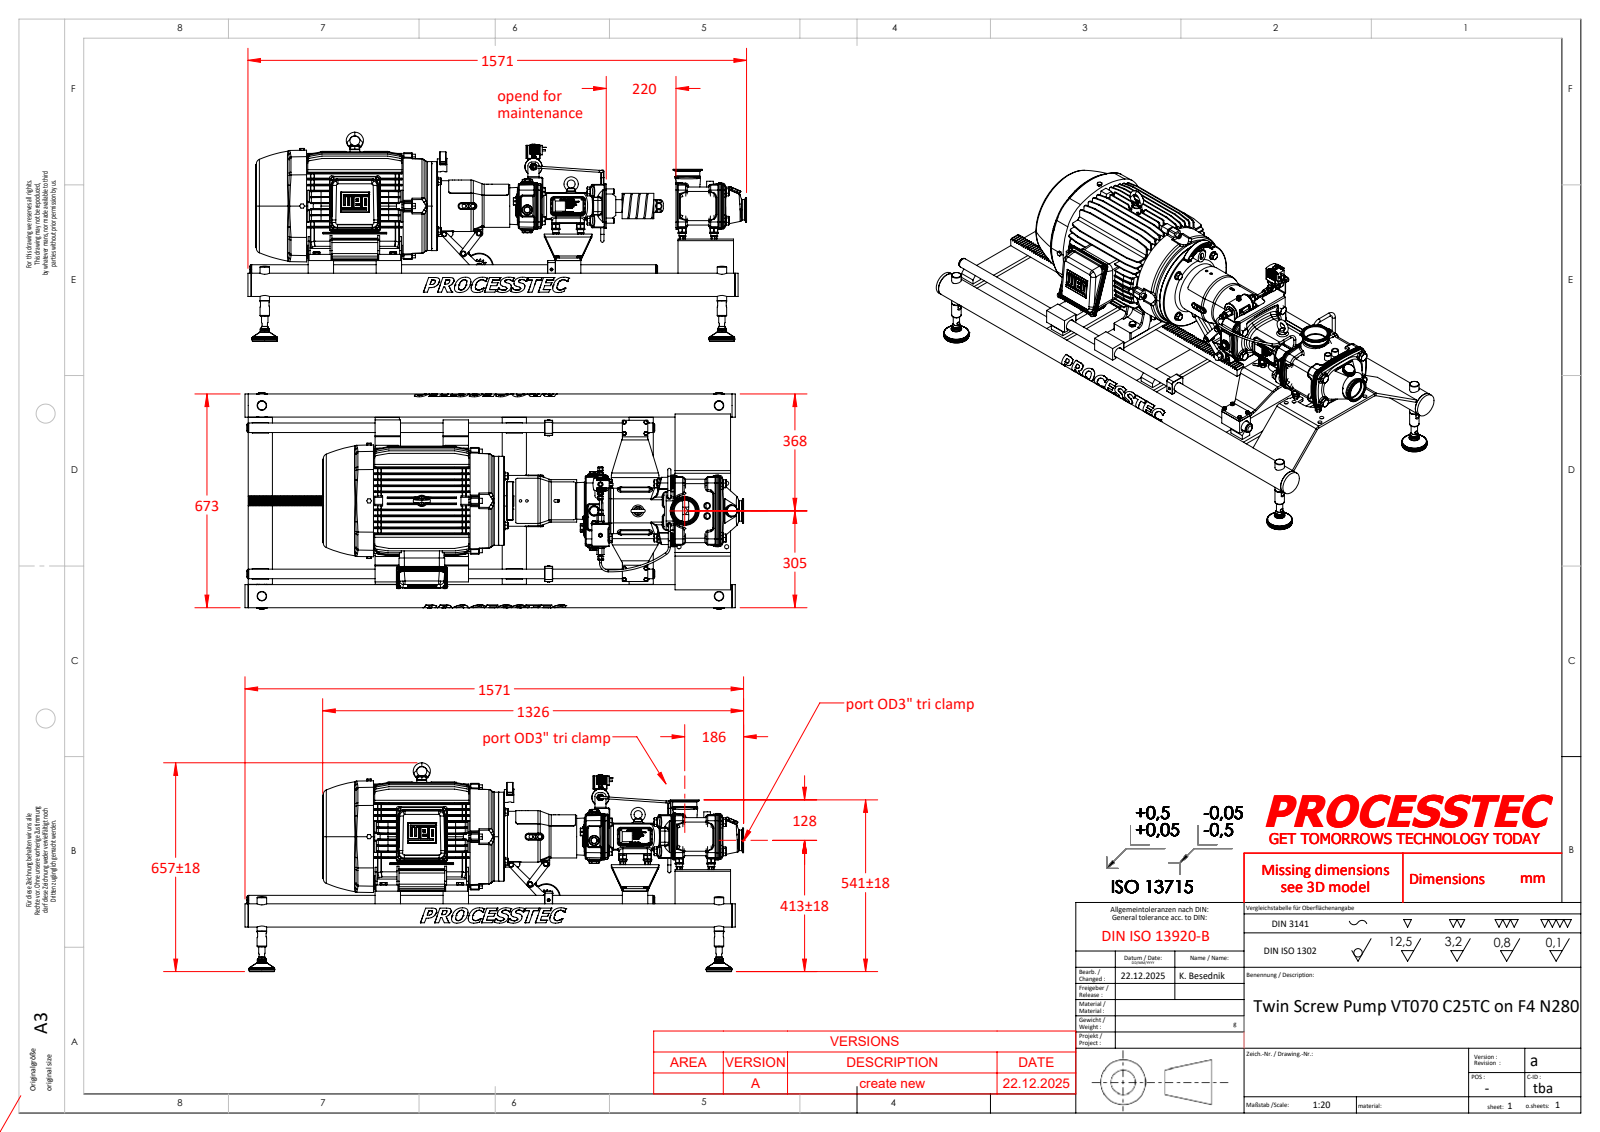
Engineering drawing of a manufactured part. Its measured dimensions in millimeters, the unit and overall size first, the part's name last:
Units: millimetres
Overall size (bounding box): 1570.5 × 680.5 × 657.46
Round holes (diameter × count): ⌀8 ×23, ⌀8.5 ×21, ⌀5 ×18, ⌀10.5 ×13, ⌀6.8 ×12, ⌀13 ×12, ⌀7.5 ×10, ⌀14 ×10, ⌀17.5 ×9, ⌀6.4 ×8, ⌀10.1 ×8, ⌀10.25 ×8
Round bosses / shafts (diameter × count): ⌀10 ×34, ⌀24 ×21, ⌀6 ×19, ⌀16 ×16, ⌀12 ×15, ⌀20 ×13, ⌀17 ×12, ⌀15 ×10
Partial cylindrical surfaces — rounded edges, fillets, slot ends (radius × count): R2 ×148, R4 ×85, R3 ×80, R0.5 ×64, R8 ×60, R1.5 ×52, R6 ×43, R5 ×40
Main face-to-face distances: 8, 12.7, 2, 17, 76.63, 59.63, 46.93, 63.93, 56, 189.19
Hole centre spacings: 461.41, 400, 230, 832.41, 41, 609.59, 800, 460
Volume: 70 050 000 mm³ · Surface area: 6 648 000 mm²
Bodies: 196 solids, 18029 faces (7301 planar, 3253 cylindrical, 7475 other)
Part name (STEP PRODUCT): 001384; 000987_Standard<Wie bearbeitet>; 001255; 001324 (+8 more)
STEP written by: SolidWorks 2023 (AUTOMOTIVE_DESIGN)
